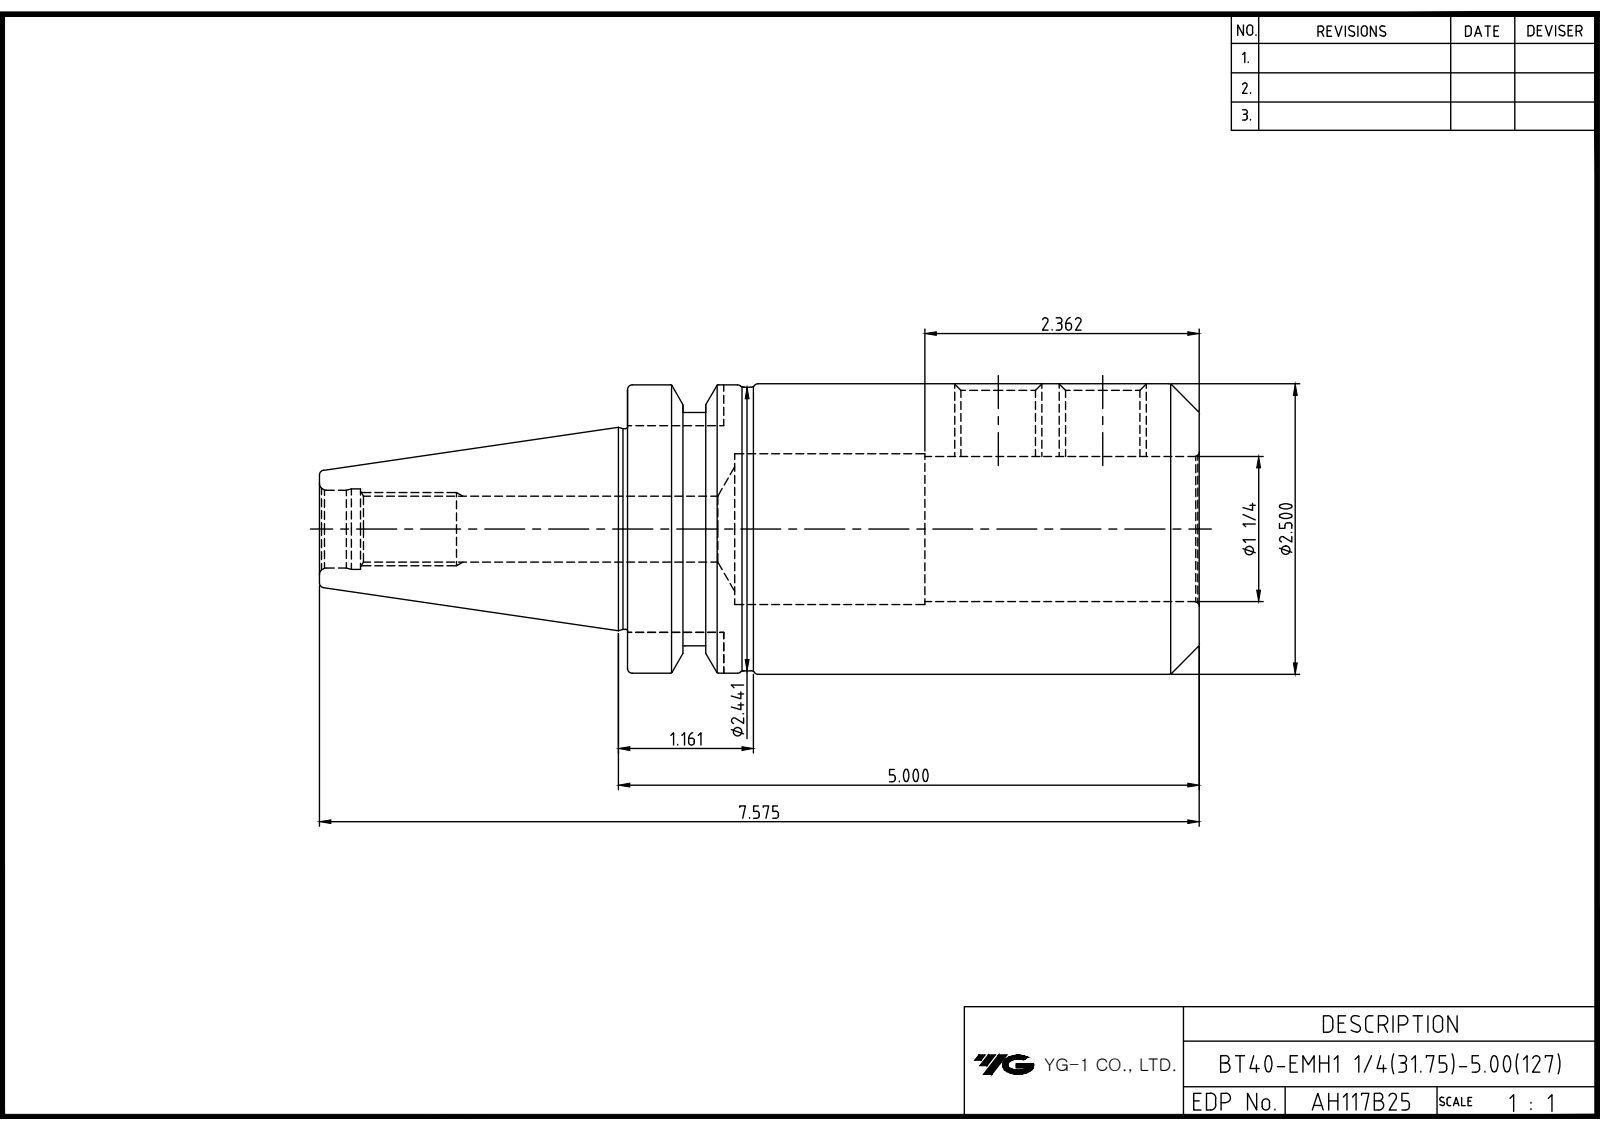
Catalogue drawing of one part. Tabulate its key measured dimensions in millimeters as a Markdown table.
| quantity | value |
| --- | --- |
| part name | LO-BT40-EMH31.75-127 |
| STEP written by | Autodesk Inventor 2022 (AUTOMOTIVE_DESIGN) |
| units | millimeters |
| bodies | 1 solid, 58 faces (16 planar, 18 cylindrical, 24 other) |
| overall size | 192.4 × 63.5 × 63.5 |
| volume | 341 181 mm³ |
| surface area | 52 690 mm² |
| round holes (diameter × count) | 17.32 × 2, 13.5 × 1, 13.84 × 1, 17 × 1, 17.6 × 1, 31.75 × 1, 32.95 × 1 |
| round bosses / shafts (diameter × count) | 63.5 × 1, 63 × 1, 62 × 1, 52.6 × 1, 44 × 1 |
| partial cylindrical surfaces (radius × count) | 8.05 × 1 |
| main face-to-face distances | 125, 45.2, 23.4, 101.6, 16.1, 67.4, 90.8, 192.4, 84.5, 17.1 |
| hole center spacings | 22.86 |
